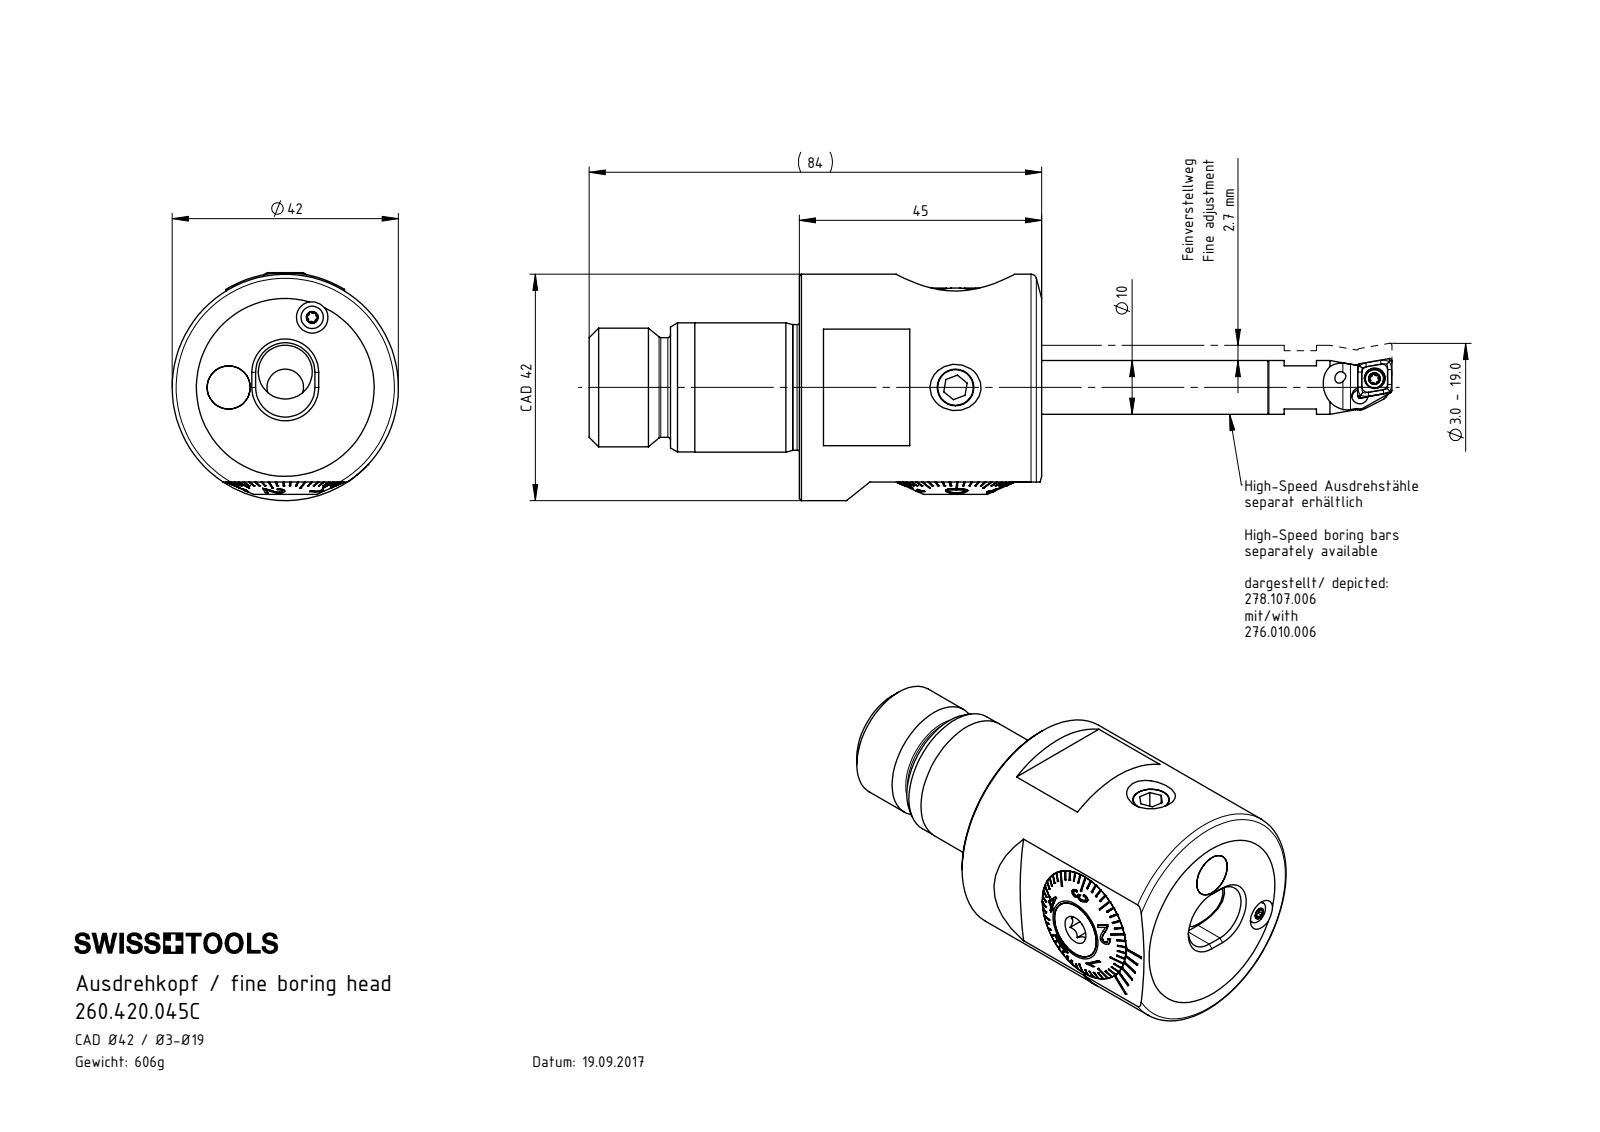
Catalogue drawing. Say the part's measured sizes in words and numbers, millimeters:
The part is named "260.420.045C; HS6-A11.K11.023; CCMT060204; WCA-ER2.001.005_A (+8 more)". Its 3-D file was written by "SolidWorks 2017 (CONFIG_CONTROL_DESIGN)". It is 19 solids with 832 faces: 338 planar, 170 cylindrical and 324 other. Overall it measures 149 by 42 by 42 millimeters. Its volume is 73 887 cubic millimeters and its surface area 30 666 square millimeters. Round holes: 4 of diameter 6.8, 2 of diameter 2, 1 of diameter 1, 1 of diameter 2.05, 1 of diameter 2.5, 1 of diameter 2.8, 1 of diameter 3.2, 1 of diameter 3.85, 1 of diameter 3.9, 1 of diameter 4, 1 of diameter 5, 1 of diameter 6. Round bosses or shafts: 3 of diameter 8, 2 of diameter 22, 1 of diameter 42, 1 of diameter 24, 1 of diameter 23.95, 1 of diameter 23.3, 1 of diameter 21.98, 1 of diameter 21.9. Partial cylindrical surfaces (rounded edges, fillets, slot ends): 12 of radius 0.21, 10 of radius 0.36, 5 of radius 3.2, 2 of radius 0.36, 2 of radius 5.5, 1 of radius 0.5, 1 of radius 1.4, 1 of radius 1.5. The main face-to-face distances are 45, 36, 2.2, 1.1, 4.5, 2.3, 5.6, 39, 4.95, 6.05. The hole center spacings are 5, 10, 10.5, 13.93, 20.23.
